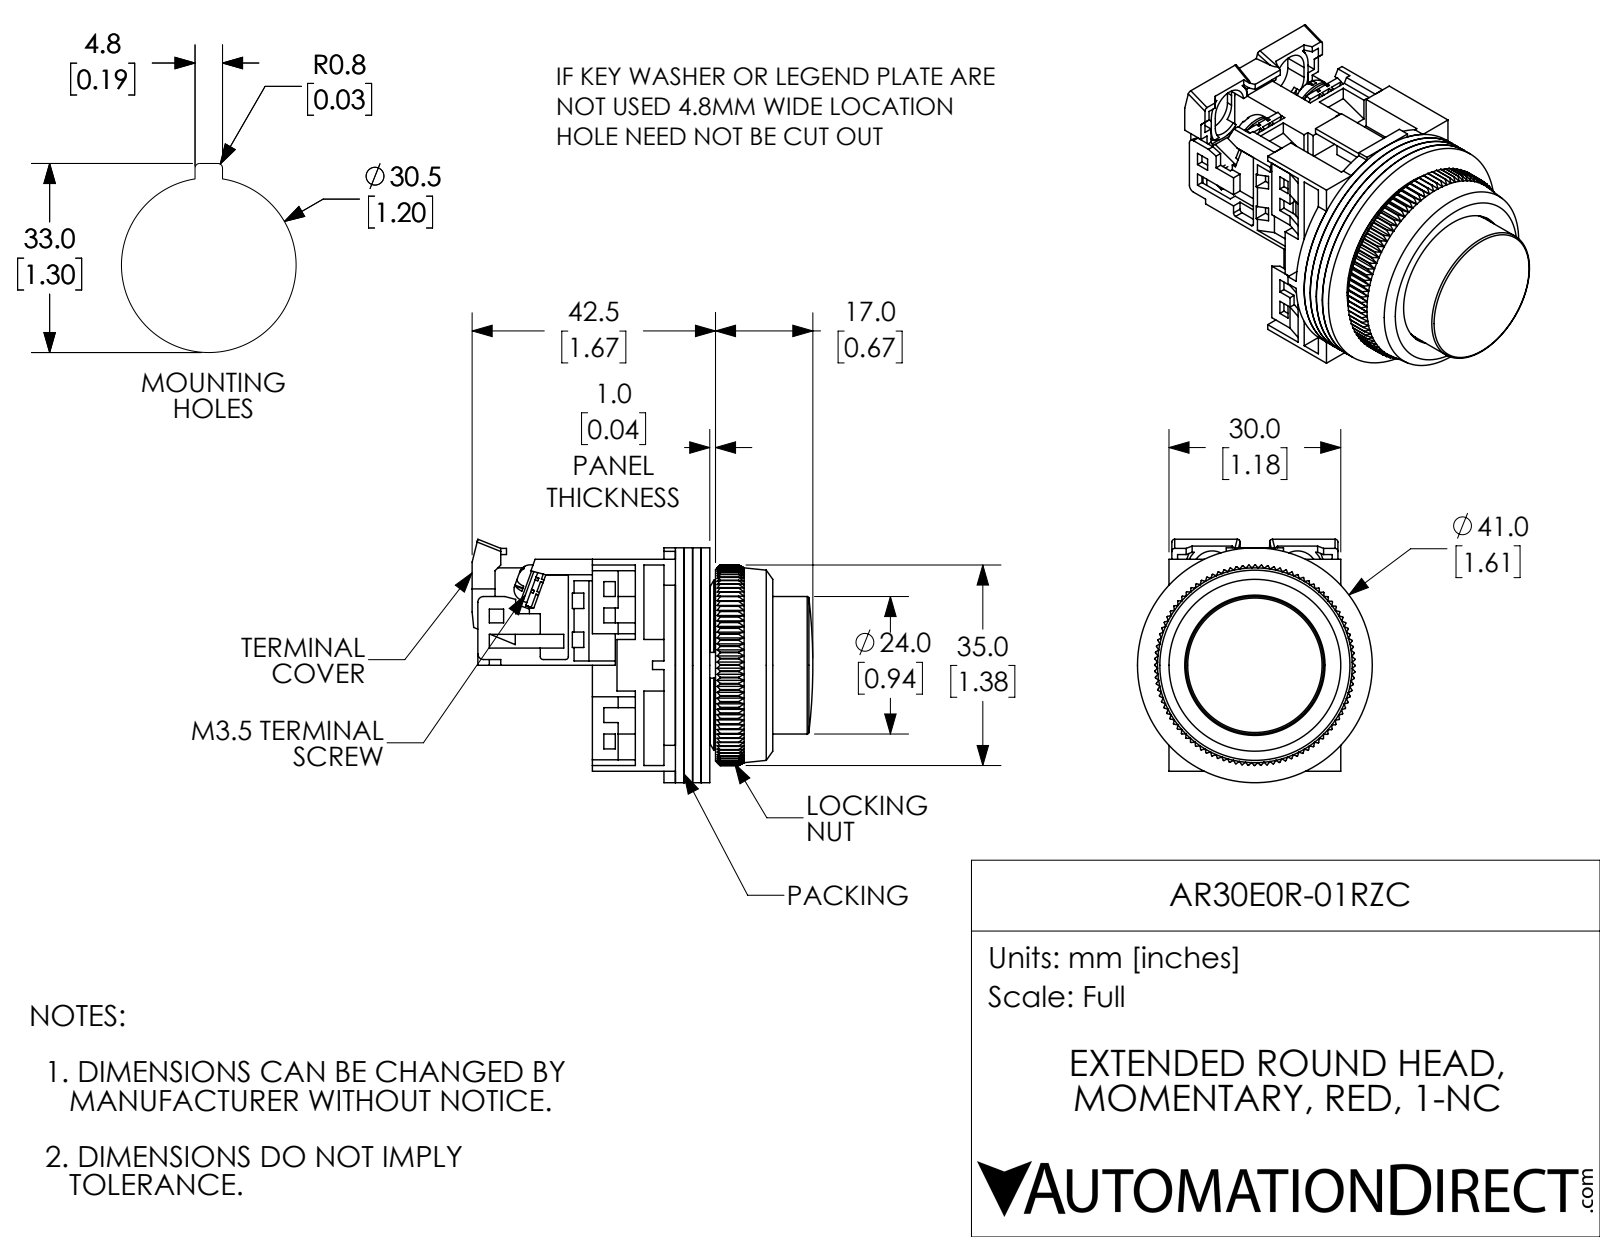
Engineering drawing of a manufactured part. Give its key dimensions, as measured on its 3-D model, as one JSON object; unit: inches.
{"part_name": "AR30E0R-01RZC", "step_written_by": "SolidWorks 2017 (AUTOMOTIVE_DESIGN)", "units": "inches", "bodies": {"solids": 16, "faces": 1234, "planar": 775, "cylindrical": 249, "other": 210}, "overall_size": [2.342, 1.673, 1.614], "volume_in3": 1.642, "surface_area_in2": 48.85, "round_holes": [[0.138, 4], [0.142, 2], [0.118, 1], [0.472, 1], [0.709, 1], [0.787, 1], [0.945, 1], [0.965, 1], [1.122, 1], [1.252, 1]], "round_bosses_or_shafts": [[0.26, 2], [0.138, 2], [1.614, 1], [1.181, 1], [0.866, 1], [0.551, 1]], "partial_cylinders_radius": [[0.059, 8], [0.02, 6], [0.039, 2], [0.138, 2], [0.177, 2], [0.118, 1], [0.398, 1], [0.449, 1]], "face_to_face_distances": [0.059, 0.118, 0.177, 0.039, 0.197, 0.079, 0.276, 0.689, 0.728, 0.602], "hole_center_spacings": [0.579, 0.61]}
